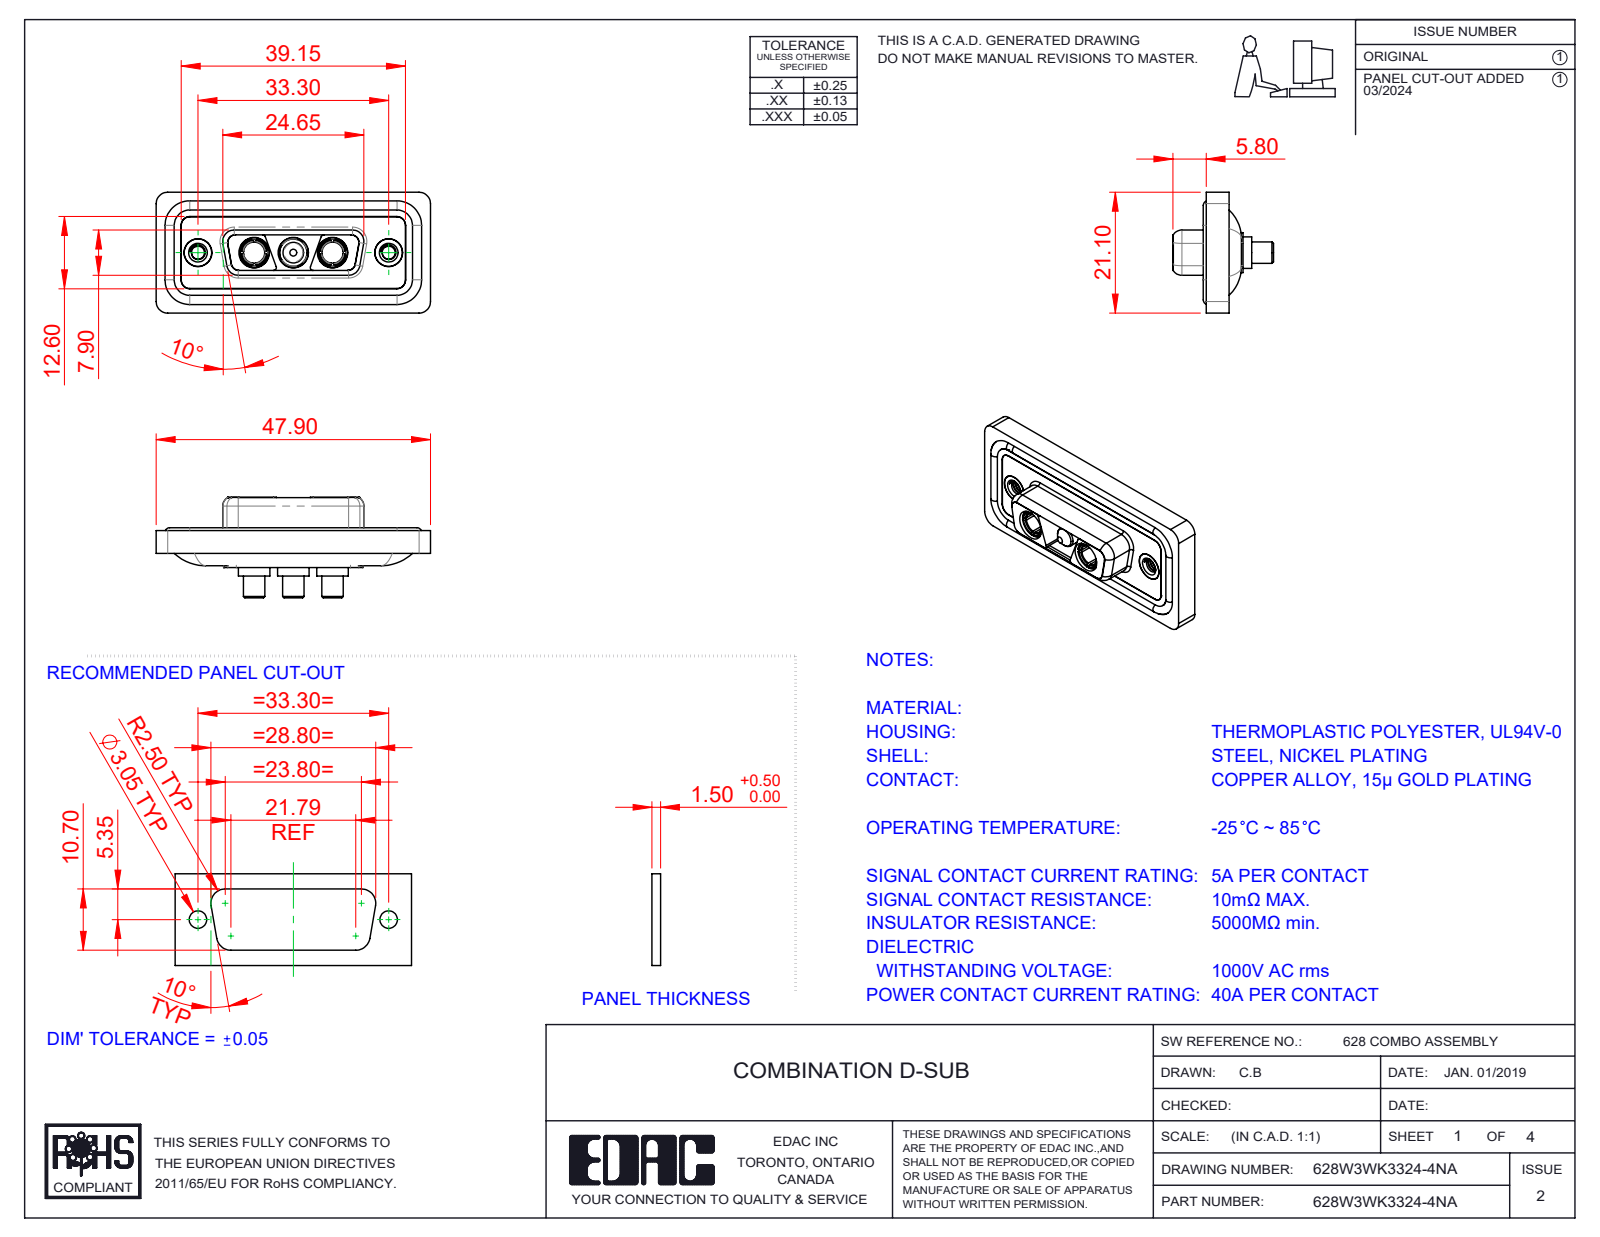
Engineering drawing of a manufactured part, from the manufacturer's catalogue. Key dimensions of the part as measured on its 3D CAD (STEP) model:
Part name (STEP PRODUCT): 628Combo Housing_3WK3; 628Combo Shell Rear_15 Contacts; 628Combo Shell Front_15 Contacts; 628W3WK3324-4NA (+4 more)
STEP written by: SolidWorks 2023 (CONFIG_CONTROL_DESIGN)
Units: millimetres
Bodies: 13 solids, 581 faces (178 planar, 260 cylindrical, 143 other)
Overall size (bounding box): 47.9 × 21.1 × 17.55
Volume: 5 935 mm³ · Surface area: 9 535 mm²
Round holes (diameter × count): ⌀4.85 ×5, ⌀5.3 ×3, ⌀2.26 ×2, ⌀3.7 ×2, ⌀4 ×2, ⌀4.05 ×2, ⌀5 ×2
Round bosses / shafts (diameter × count): ⌀1.6 ×4, ⌀5.5 ×3, ⌀5.2 ×3, ⌀4.75 ×3, ⌀3.75 ×3, ⌀4.96 ×2, ⌀4.95 ×2, ⌀4.8 ×2
Partial cylindrical surfaces — rounded edges, fillets, slot ends (radius × count): R1.5 ×22, R2 ×20, R1.35 ×12, R0.5 ×8, R1.6 ×8, R0.25 ×4, R0.6 ×4, R0.65 ×4
Main face-to-face distances: 0.4, 1.6, 0.5, 1.8, 1.1, 2.9, 5.65, 7.05, 5.35, 1.5
Hole centre spacings: 6.85, 9.8, 16.65, 23.5, 13.7, 33.3
